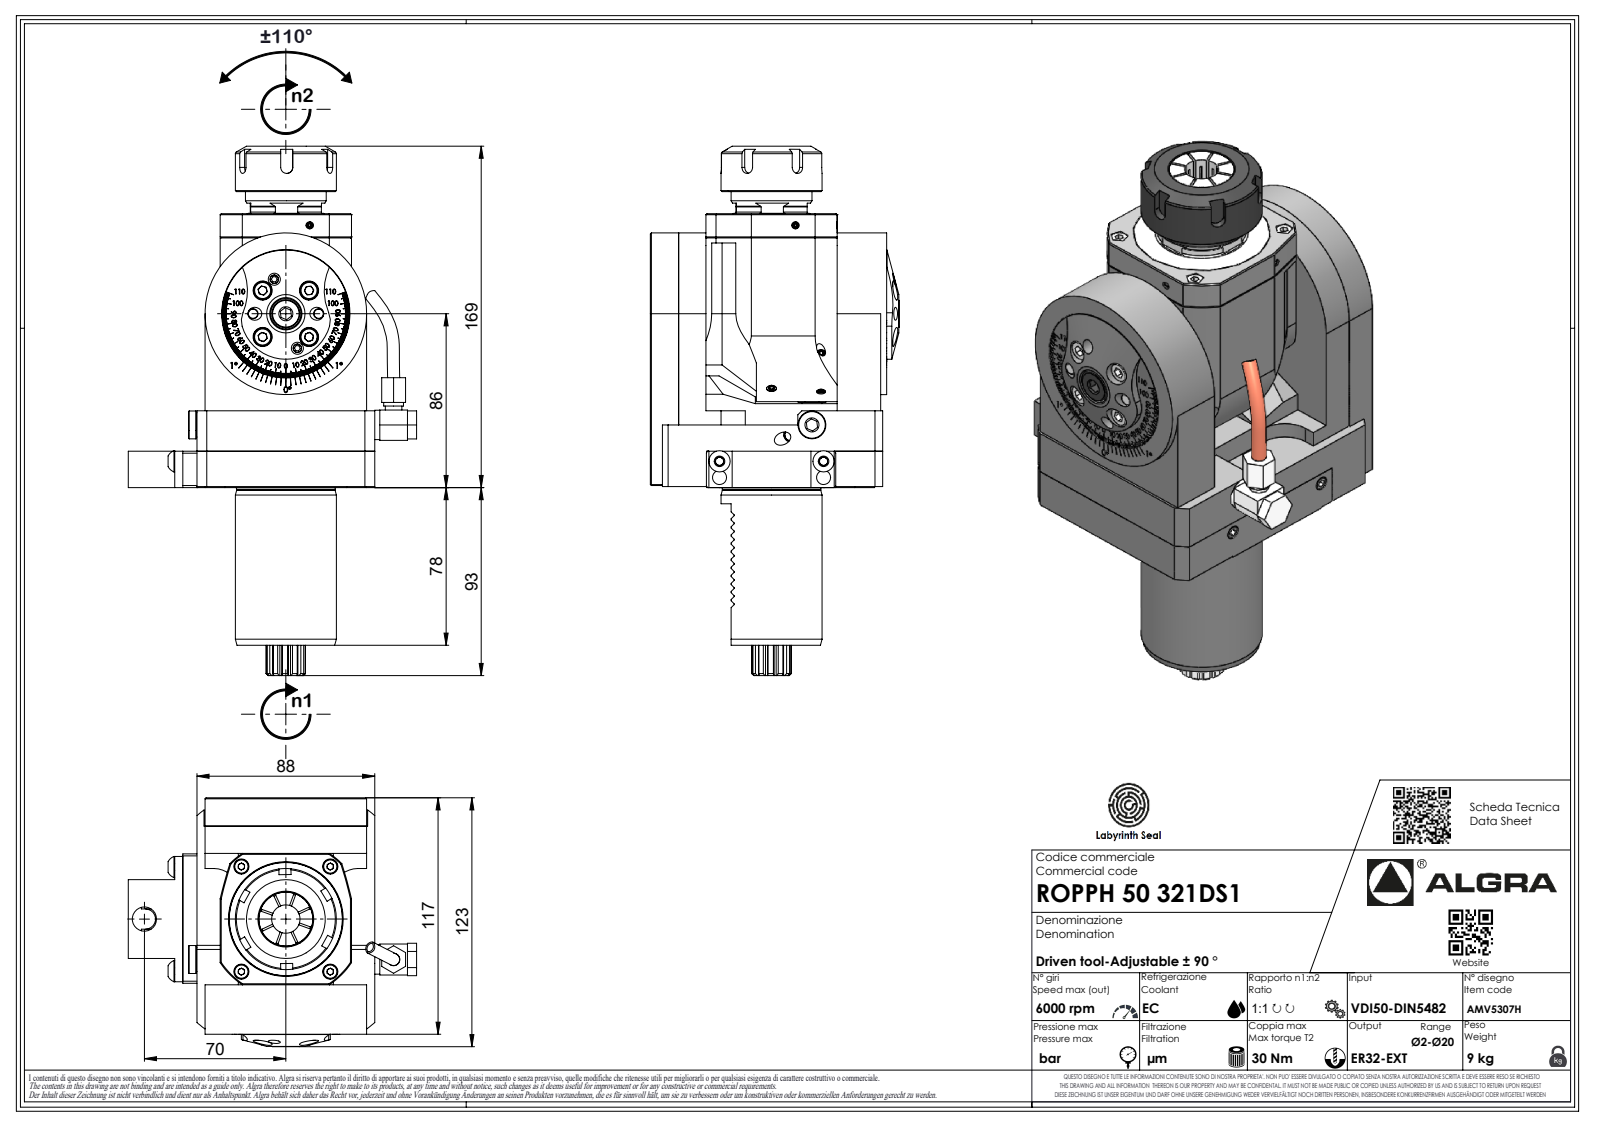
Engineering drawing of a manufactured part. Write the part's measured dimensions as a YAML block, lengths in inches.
part_name: "ROPPH50321DS1"
step_written_by: "SolidWorks 2023 (AUTOMOTIVE_DESIGN)"
units: inches
bodies: {solids: 1, faces: 669, planar: 390, cylindrical: 142, other: 137}
overall_size: [10.311, 5.618, 4.843]
volume: 78.11
surface_area: 173.7
round_holes:
  - {diameter: 0.083, count: 1}
round_bosses_or_shafts:
  - {diameter: 3.15, count: 1}
  - {diameter: 1.969, count: 1}
  - {diameter: 1.917, count: 1}
  - {diameter: 1.575, count: 1}
  - {diameter: 0.571, count: 1}
  - {diameter: 0.386, count: 1}
  - {diameter: 0.323, count: 1}
  - {diameter: 0.251, count: 1}
partial_cylinders:
  - {radius: 0.369, count: 24}
  - {radius: 0.012, count: 12}
  - {radius: 0.013, count: 7}
  - {radius: 0.02, count: 7}
  - {radius: 0.146, count: 7}
  - {radius: 0.118, count: 5}
  - {radius: 0.039, count: 4}
  - {radius: 0.394, count: 2}
face_to_face_distances: [0.157, 2.559, 3.307, 0.02, 3.012, 0.453, 0.886, 1.083, 0.295, 2.854]
